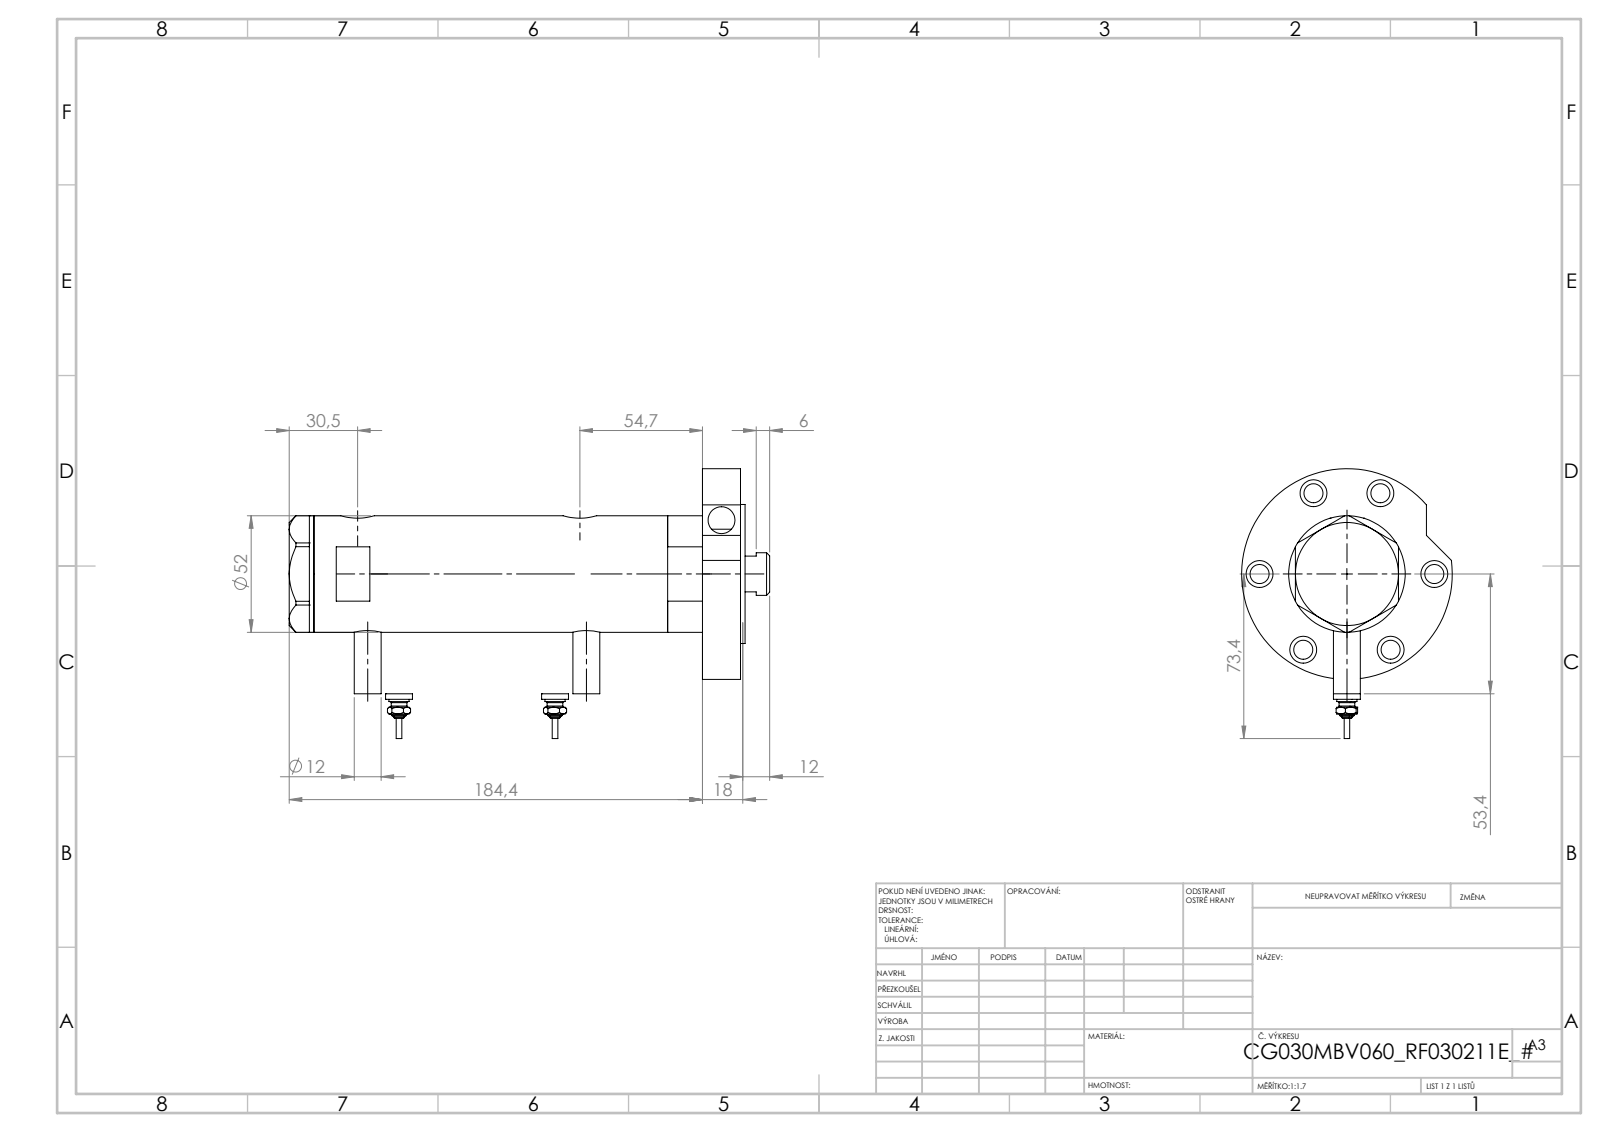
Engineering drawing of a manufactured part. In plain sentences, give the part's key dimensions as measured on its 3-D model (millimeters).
The part is named "V270CG_FRONT; V270CG_SWITCH; V270CG_BACK; V270CG_RF211E (+2 more)". Its 3-D file was written by "SolidWorks 2019 (CONFIG_CONTROL_DESIGN)". It is 7 solids with 290 faces: 106 planar, 110 cylindrical and 74 other. Overall it measures 209.02 by 105.3 by 94 millimeters. Its volume is 456 048 cubic millimeters and its surface area 110 044 square millimeters. Round holes: 7 of diameter 12, 6 of diameter 8.5, 2 of diameter 5, 2 of diameter 9.73, 2 of diameter 12.5, 2 of diameter 15, 1 of diameter 6.5, 1 of diameter 20, 1 of diameter 21.5, 1 of diameter 30, 1 of diameter 33, 1 of diameter 40. Round bosses or shafts: 3 of diameter 12, 2 of diameter 9, 2 of diameter 7, 2 of diameter 4.34, 2 of diameter 2.4, 1 of diameter 94, 1 of diameter 62, 1 of diameter 52. The main face-to-face distances are 17, 51.9, 2, 68.9, 70.9, 19, 23.8, 124.55, 176.45, 193.45. The hole center spacings are 39, 2.9, 4.5, 43.34, 64.85, 67.55, 69.95, 77.83.
